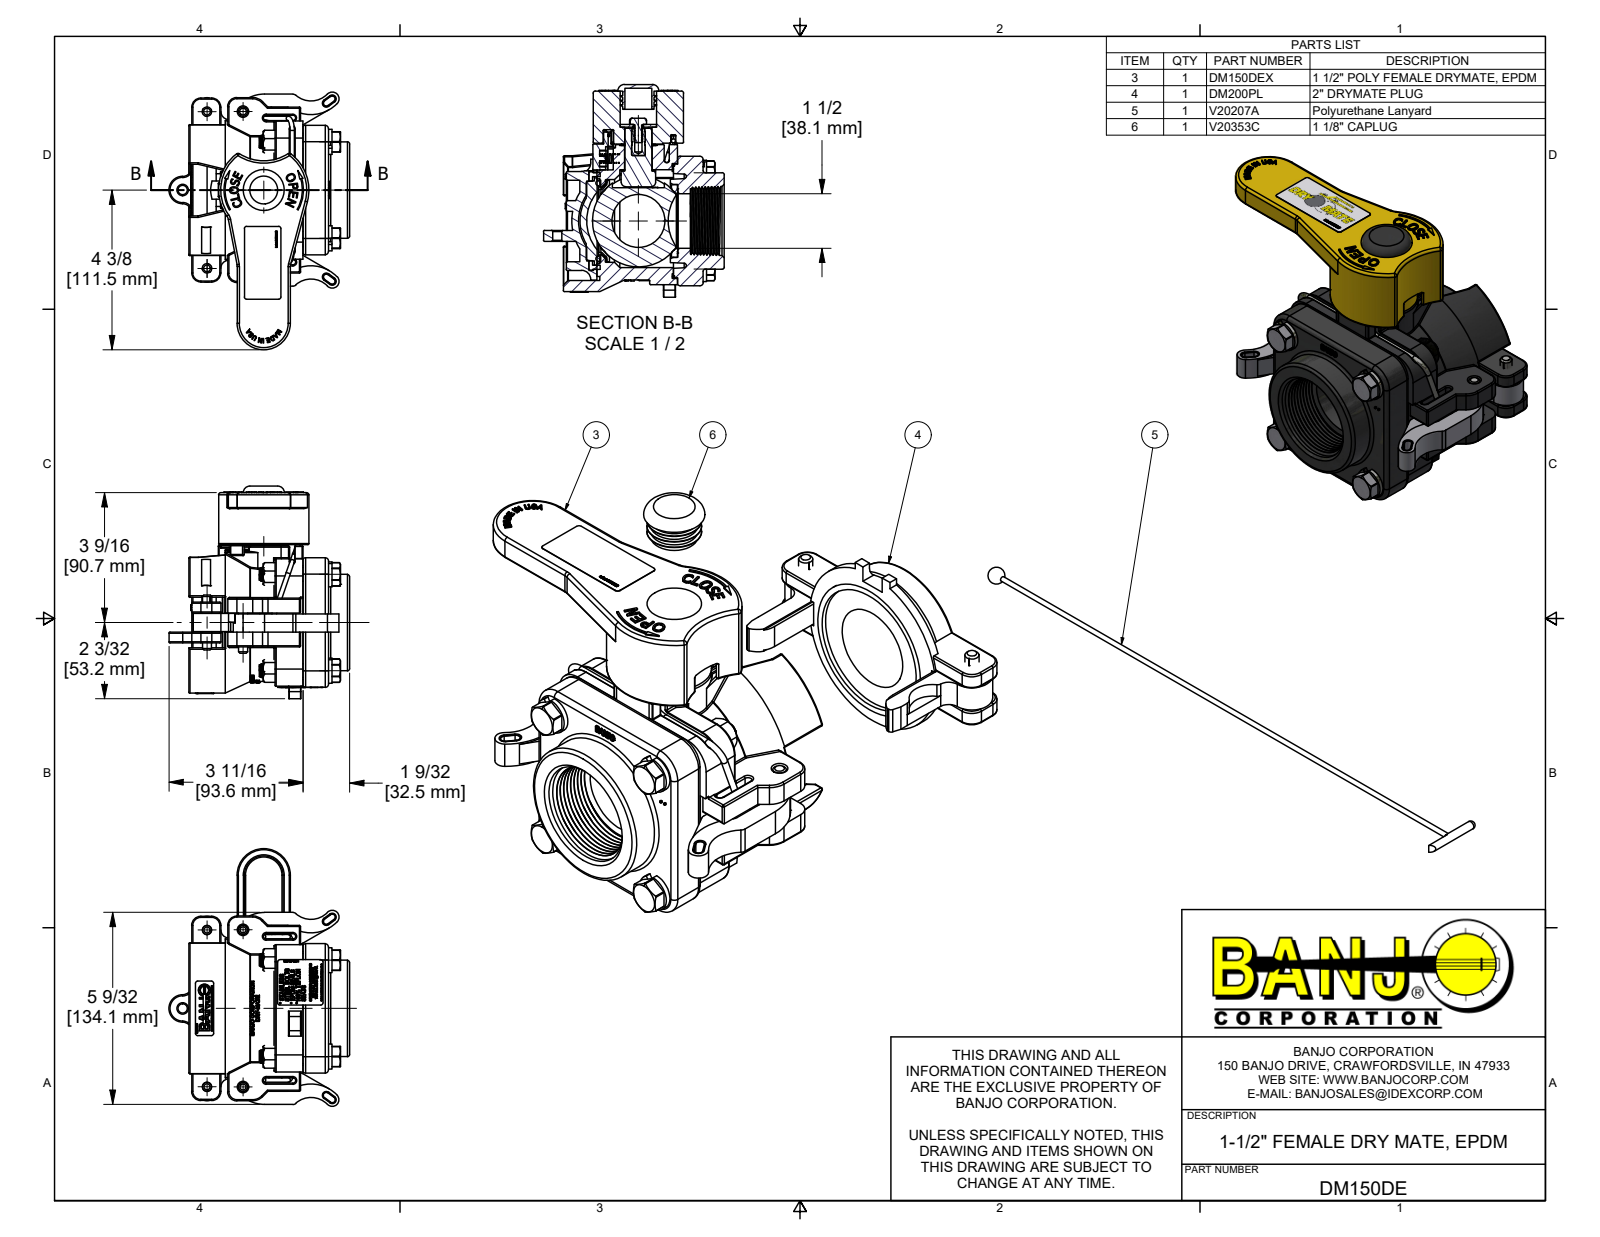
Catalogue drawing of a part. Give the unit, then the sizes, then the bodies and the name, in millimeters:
Units: millimetres
Overall size (bounding box): 179.9 × 148.5 × 126.2
Round holes (diameter × count): ⌀6.4 ×5, ⌀9.5 ×5, ⌀6.5 ×4, ⌀7.8 ×4, ⌀9.8 ×4, ⌀10.4 ×4, ⌀10.7 ×4, ⌀3.2 ×3, ⌀5 ×1, ⌀5.1 ×1, ⌀5.8 ×1, ⌀7.1 ×1
Round bosses / shafts (diameter × count): ⌀8.2 ×60, ⌀3 ×5, ⌀17.4 ×4, ⌀9.5 ×4, ⌀6.6 ×4, ⌀6.3 ×4, ⌀7.1 ×3, ⌀82.6 ×1
Partial cylindrical surfaces — rounded edges, fillets, slot ends (radius × count): R0.8 ×159, R0.3 ×41, R1.5 ×35, R0.5 ×20, R6.4 ×11, R3 ×10, R2 ×8, R2.3 ×8
Main face-to-face distances: 2.8, 23.4, 56.3, 7.6, 0.3, 74.2, 12.7, 97.4, 79.8, 17.8
Hole centre spacings: 67.4, 47.5, 47.8, 67.3, 67.6, 95.3, 24.1, 25.2
Volume: 755 600 mm³ · Surface area: 258 800 mm²
Bodies: 45 solids, 6619 faces (3059 planar, 1048 cylindrical, 2512 other)
Part name (STEP PRODUCT): DM150DE; DM150DEX; DM20254F; DM20254FY (+8 more)
STEP written by: Autodesk Inventor 2022 (AUTOMOTIVE_DESIGN)
